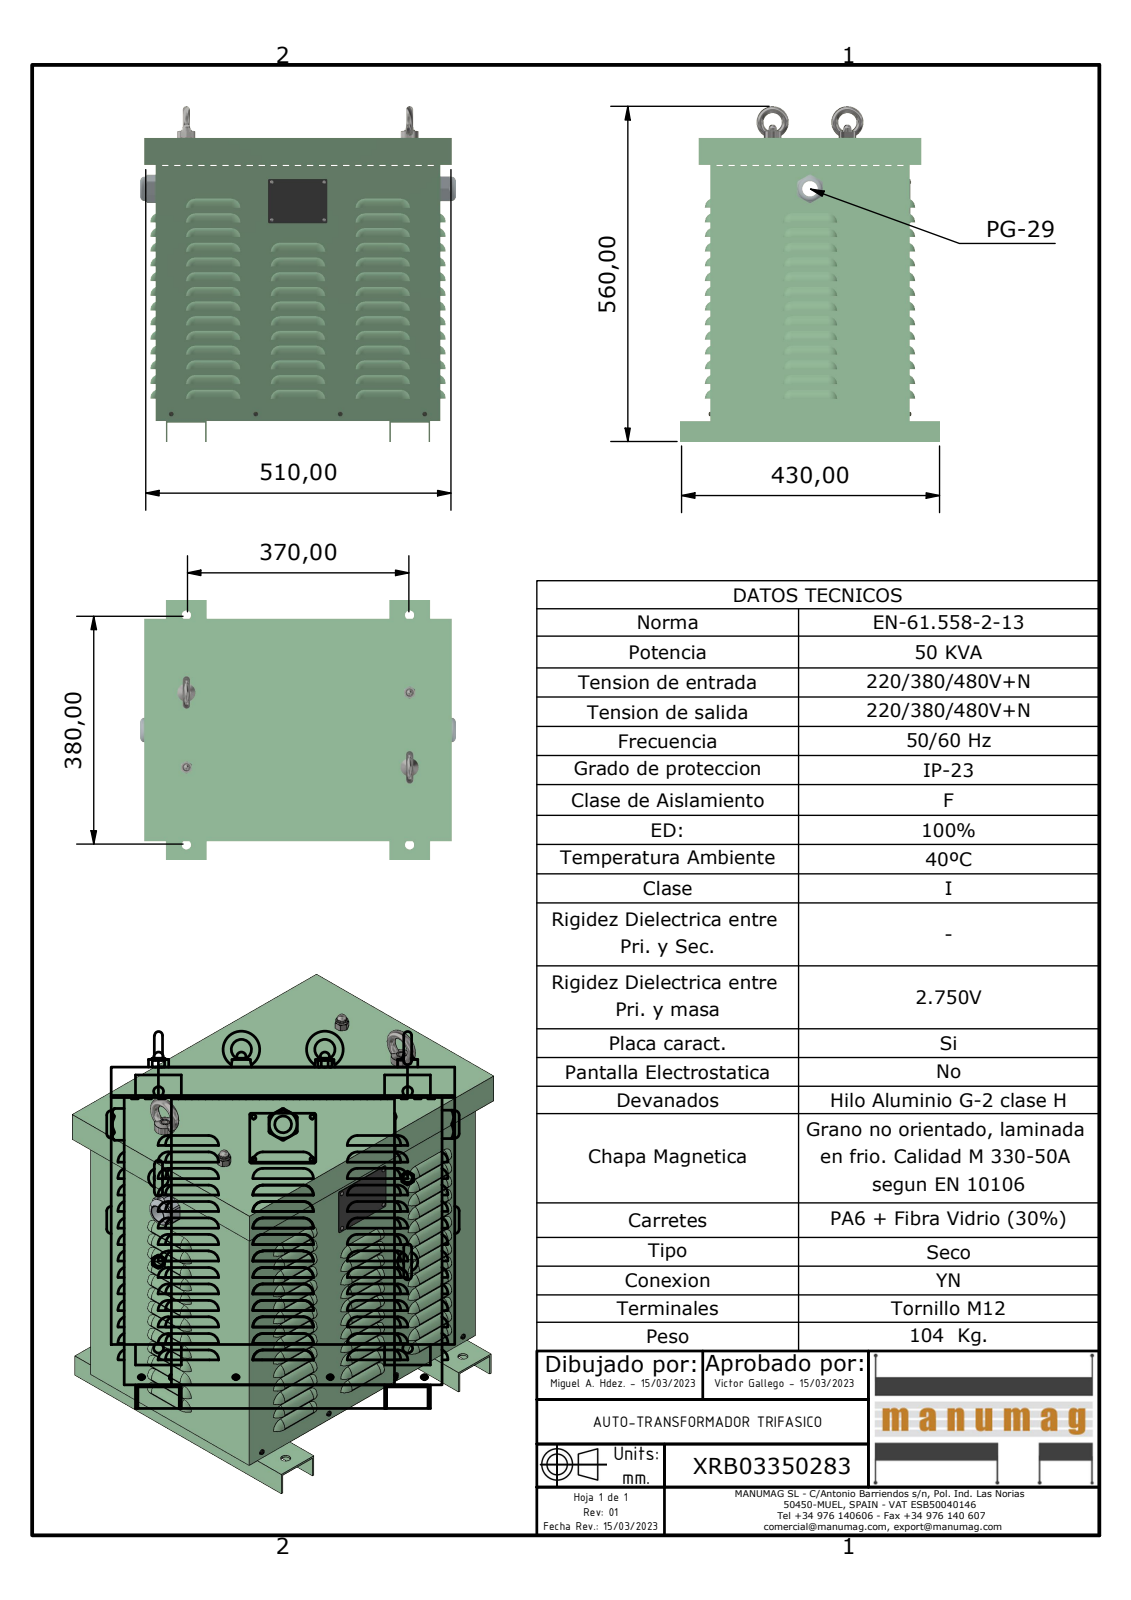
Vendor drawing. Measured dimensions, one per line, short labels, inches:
name: XRB03350283; JE040 - JE050 CUERPO; JE040 - JE050 BASE; JE040 - JE050 PATAS (+7 more)
written by: Autodesk Inventor 2023 (AUTOMOTIVE_DESIGN)
unit: in
bodies: 24 solids, 2403 faces (969 planar, 808 cylindrical, 626 other)
size: 22.047 × 20.606 × 16.969
volume: 190.1 in³; area: 4 290 in²
holes: 260× ⌀0.433, 4× ⌀0.157, 4× ⌀0.197, 4× ⌀0.398, 4× ⌀0.551, 4× ⌀0.591, 1× ⌀0.984, 1× ⌀1.496
bosses: 4× ⌀0.157, 4× ⌀0.143, 4× ⌀0.126, 2× ⌀1.181, 2× ⌀0.709, 2× ⌀0.535, 1× ⌀1.606, 1× ⌀1.469
rounds: 104× R0.551, 54× R0.276, 54× R0.591, 12× R0.127, 8× R0.098, 8× R0.295, 4× R0.079, 1× R0.939
face distances: 0.079, 18.504, 18.583, 12.953, 18.425, 12.874, 13.031, 0.118, 0.768, 13.72
hole spacings: 1.25, 2.819, 0.591, 1.102, 2.756, 1.756, 3.903, 5.543
